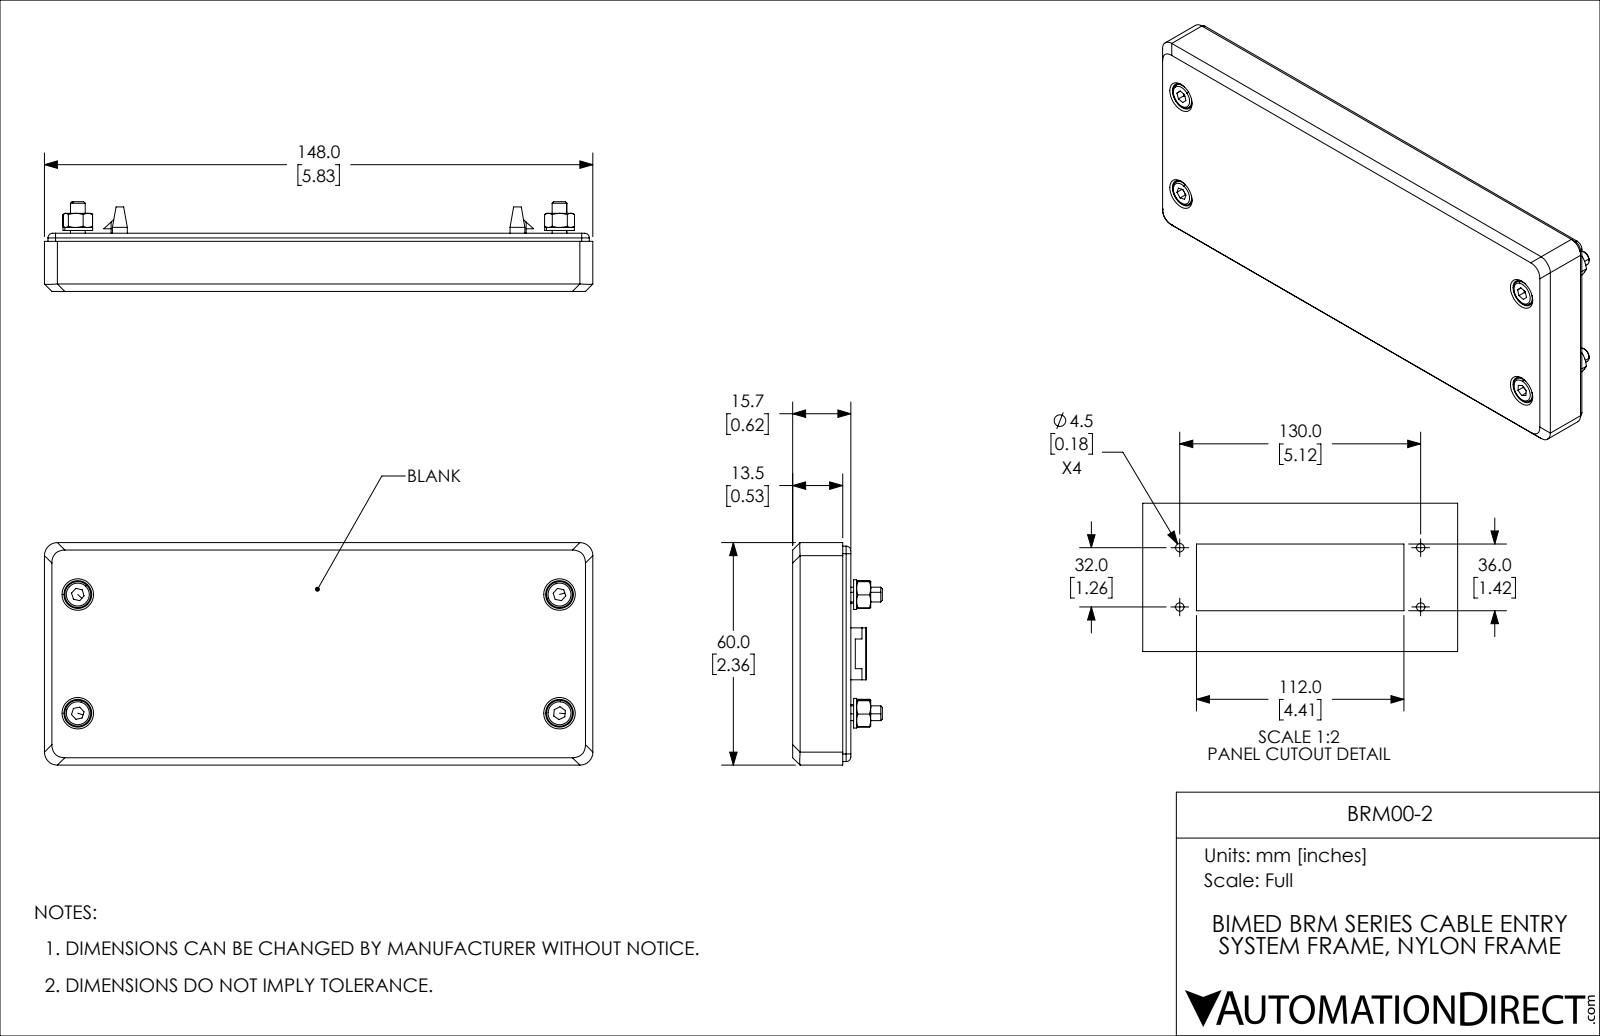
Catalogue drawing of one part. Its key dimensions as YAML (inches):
part_name: "BRM00-2"
step_written_by: "SolidWorks 2021 (CONFIG_CONTROL_DESIGN)"
units: inches
bodies: {solids: 17, faces: 1009, planar: 267, cylindrical: 400, other: 342}
overall_size: [5.827, 2.362, 0.953]
volume: 3.934
surface_area: 88.47
round_holes:
  - {diameter: 0.472, count: 23}
  - {diameter: 0.11, count: 14}
  - {diameter: 0.098, count: 4}
  - {diameter: 0.128, count: 4}
  - {diameter: 0.169, count: 4}
  - {diameter: 0.177, count: 4}
  - {diameter: 0.295, count: 4}
round_bosses_or_shafts:
  - {diameter: 0.098, count: 16}
  - {diameter: 0.157, count: 8}
  - {diameter: 0.315, count: 4}
  - {diameter: 0.276, count: 4}
partial_cylinders:
  - {radius: 0.039, count: 60}
  - {radius: 0.049, count: 8}
  - {radius: 0.197, count: 8}
  - {radius: 0.02, count: 6}
  - {radius: 0.079, count: 4}
  - {radius: 0.081, count: 4}
  - {radius: 0.138, count: 4}
  - {radius: 0.195, count: 4}
face_to_face_distances: [0.098, 0.167, 0.228, 0.157, 2.195, 0.327, 0.386, 0.484, 2.028, 2.362]
hole_center_spacings: [1.732, 0.504, 0.447, 0.472, 0.591, 0.63, 0.702, 0.75]
